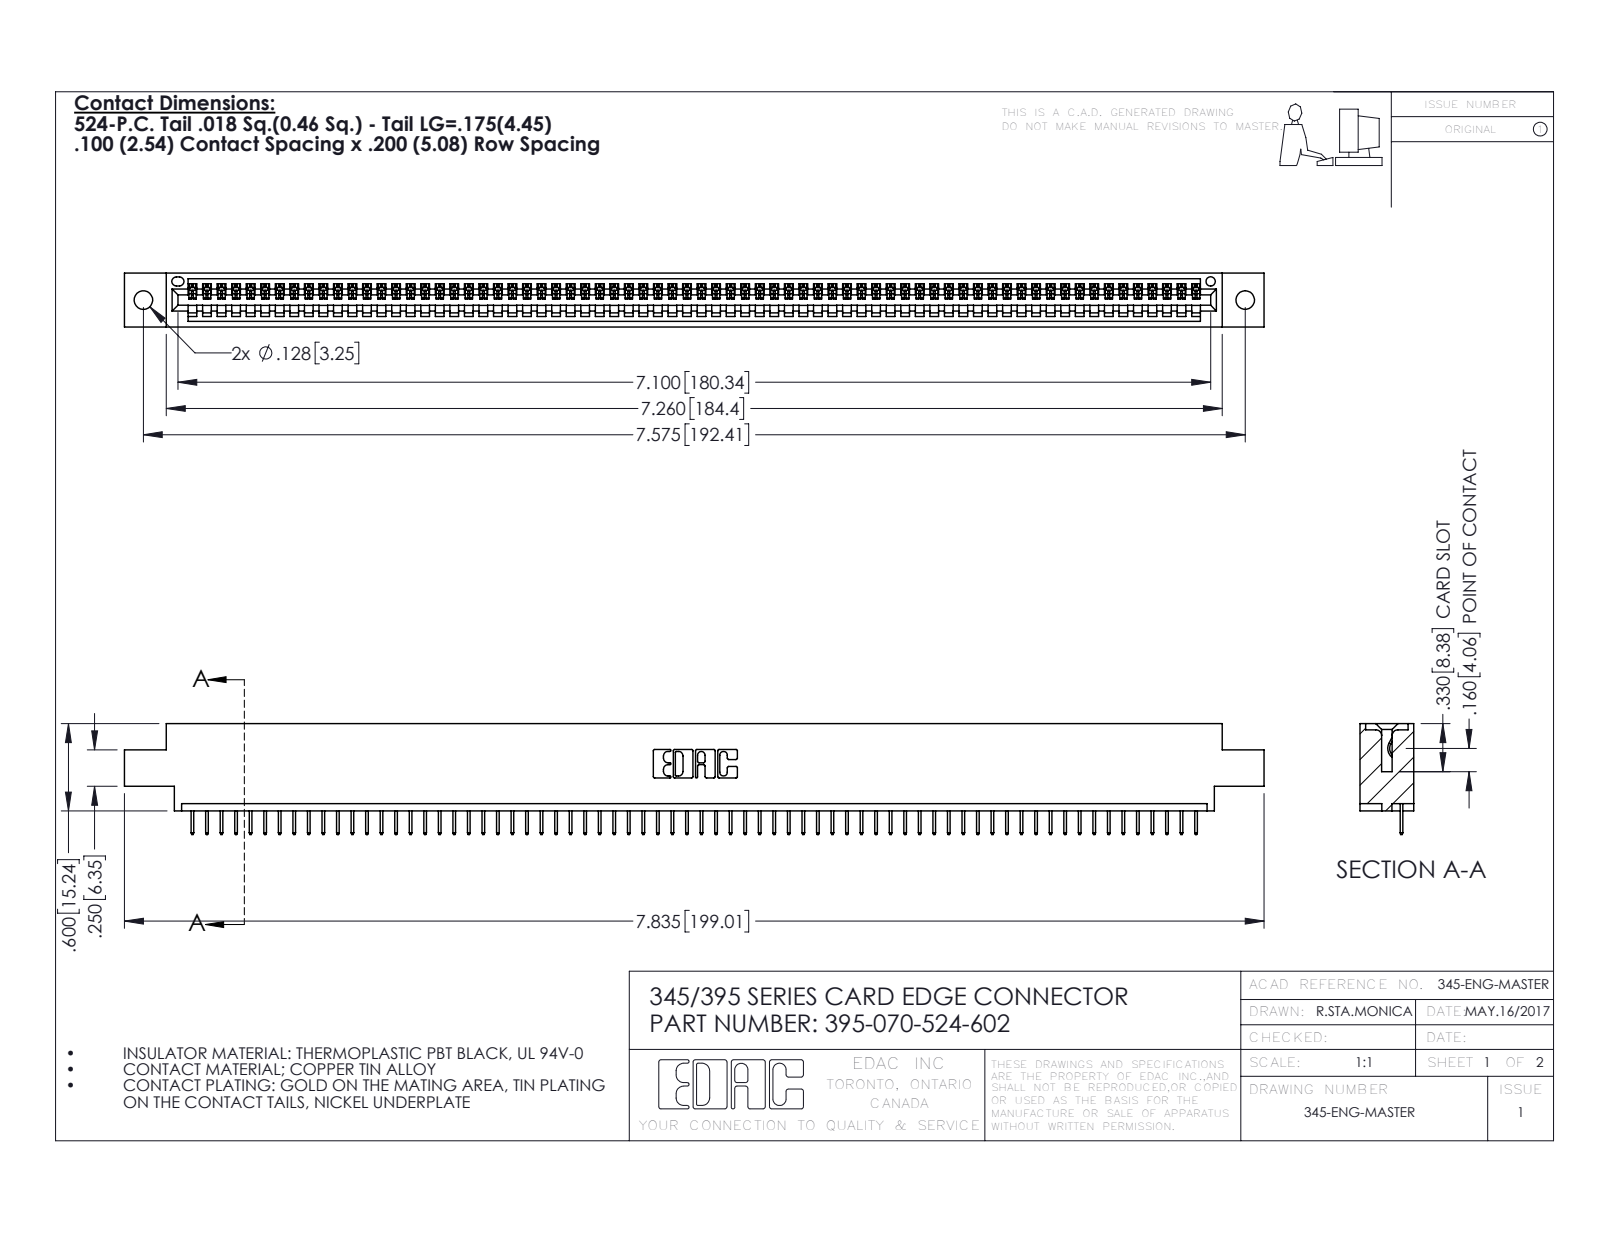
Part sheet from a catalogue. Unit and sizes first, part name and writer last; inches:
Units: inches
Overall size (bounding box): 7.835 × 0.762 × 0.37
Round holes (diameter × count): ⌀0.128 ×2, ⌀0.064 ×1
Partial cylindrical surfaces — rounded edges, fillets, slot ends (radius × count): R0.006 ×140, R0.01 ×22, R0.007 ×6, R0.031 ×6, R0.026 ×3, R0.031 ×2, R0.04 ×2, R0.014 ×1
Main face-to-face distances: 0.072, 0.298, 0.37, 0.2, 0.098, 0.272, 0.025, 0.225, 0.072, 0.175
Hole centre spacings: 0.27, 7.339, 7.575
Volume: 1.141 in³ · Surface area: 37.52 in²
Bodies: 71 solids, 4470 faces (3304 planar, 1166 cylindrical, 0 other)
Part name (STEP PRODUCT): 395-070-524-602; 345-292-001_345-293-124; 345 Part_0.170 Offset - 0.128 Dia
STEP written by: SolidWorks 2016 (CONFIG_CONTROL_DESIGN)
